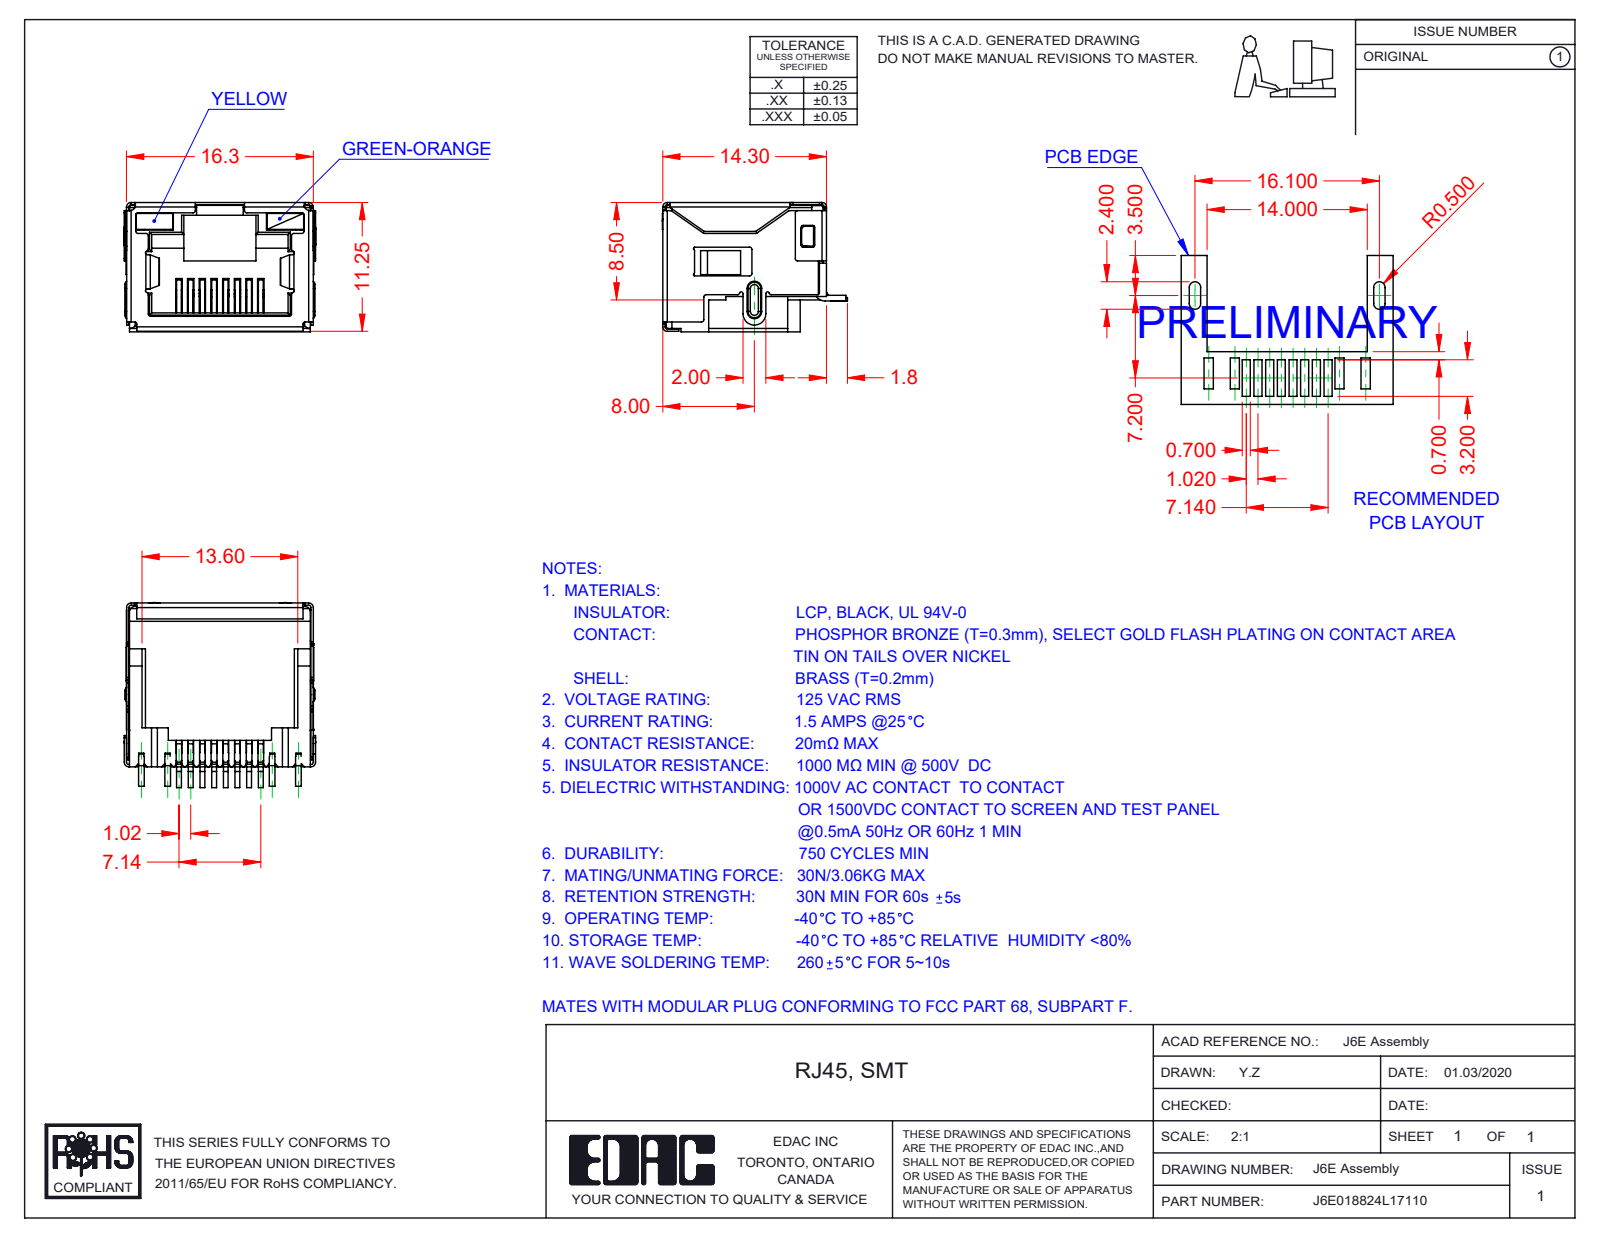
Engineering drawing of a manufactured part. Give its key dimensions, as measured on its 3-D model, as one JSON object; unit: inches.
{"part_name": "6E Shield_LED; 6E Contacts; J6E018824L17110; 6E Insulator_LED (+2 more)", "step_written_by": "SolidWorks 2016 (CONFIG_CONTROL_DESIGN)", "units": "inches", "bodies": {"solids": 12, "faces": 1498, "planar": 1099, "cylindrical": 349, "other": 50}, "overall_size": [0.659, 0.636, 0.445], "volume_in3": 0.068, "surface_area_in2": 6.27, "partial_cylinders_radius": [[0.008, 82], [0.01, 17], [0.016, 13], [0.02, 13], [0.004, 10], [0.006, 7], [0.012, 4], [0.039, 3]], "face_to_face_distances": [0.435, 0.632, 0.634, 0.624, 0.437, 0.445, 0.094, 0.028, 0.388, 0.019]}
